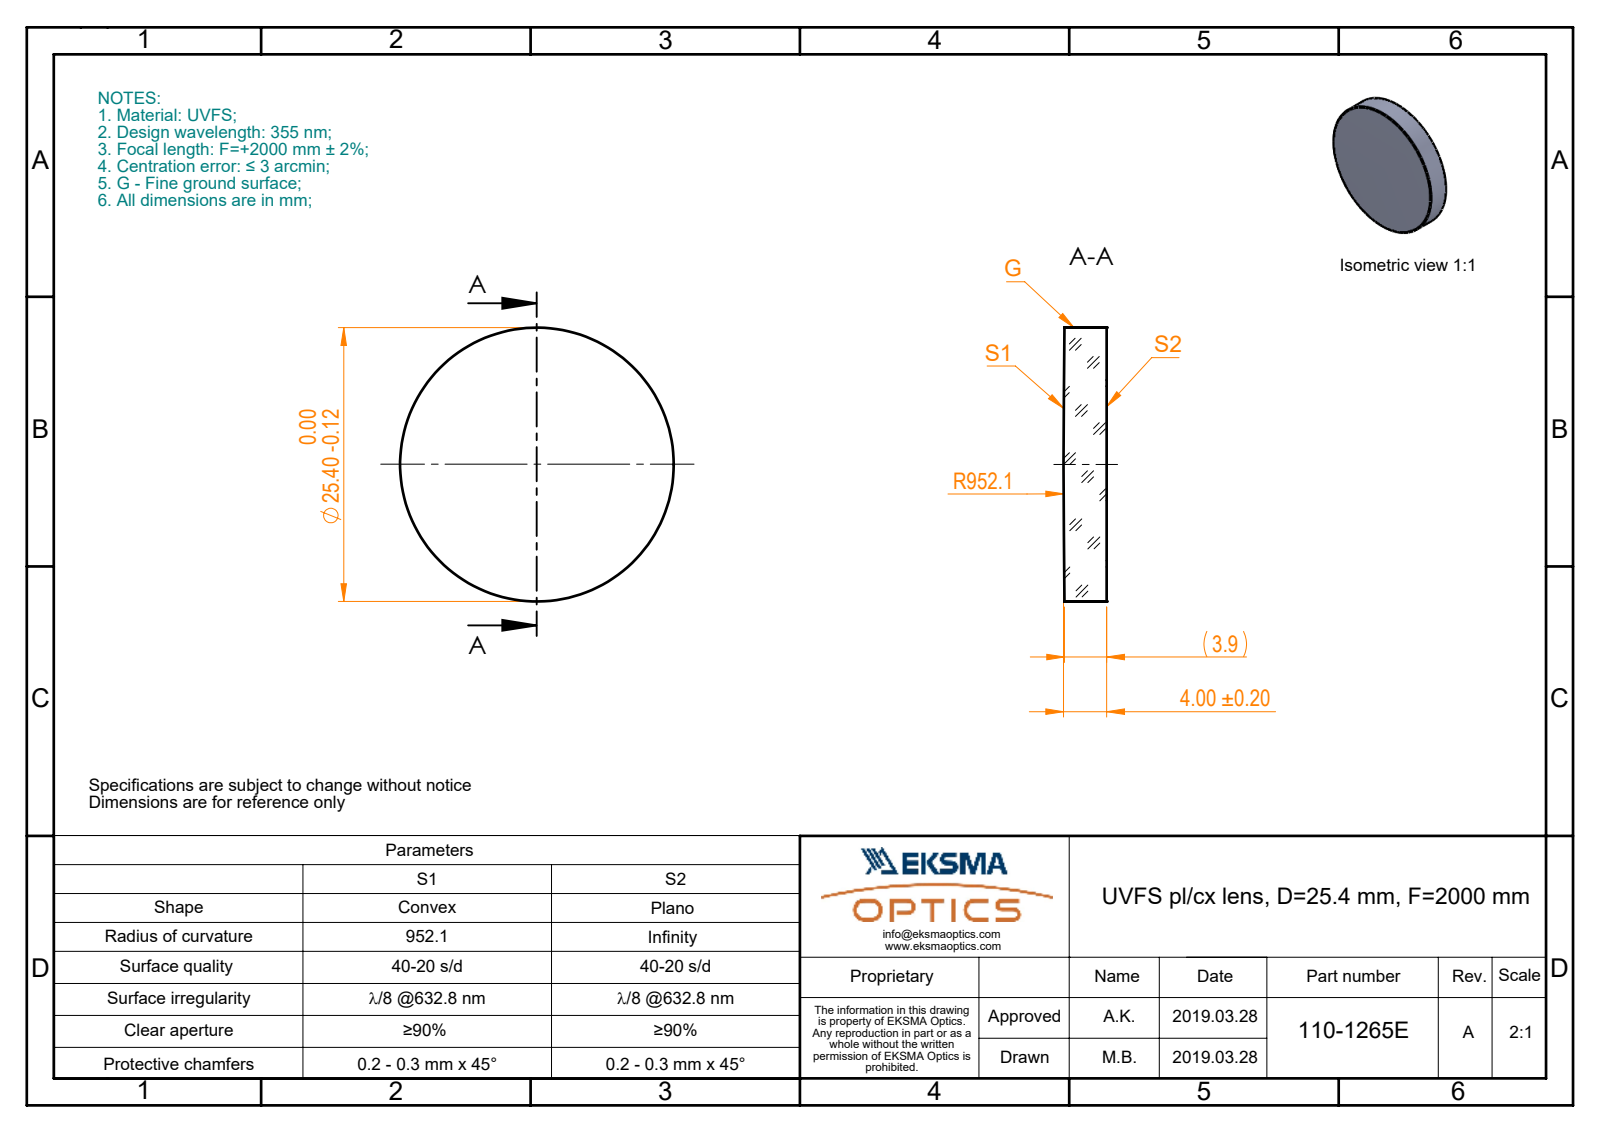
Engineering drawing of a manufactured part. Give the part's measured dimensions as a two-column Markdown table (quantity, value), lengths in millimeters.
| quantity | value |
| --- | --- |
| part name | 110-1265E UVFS pl-cx 25.4 F2000 |
| STEP written by | SolidWorks 2017 (CONFIG_CONTROL_DESIGN) |
| units | millimeters |
| bodies | 1 solid, 5 faces (1 planar, 2 cylindrical, 2 other) |
| overall size | 25.4 × 25.4 × 4 |
| volume | 2 005 mm³ |
| surface area | 1 326 mm² |
| round bosses / shafts (diameter × count) | 25.4 × 1 |
